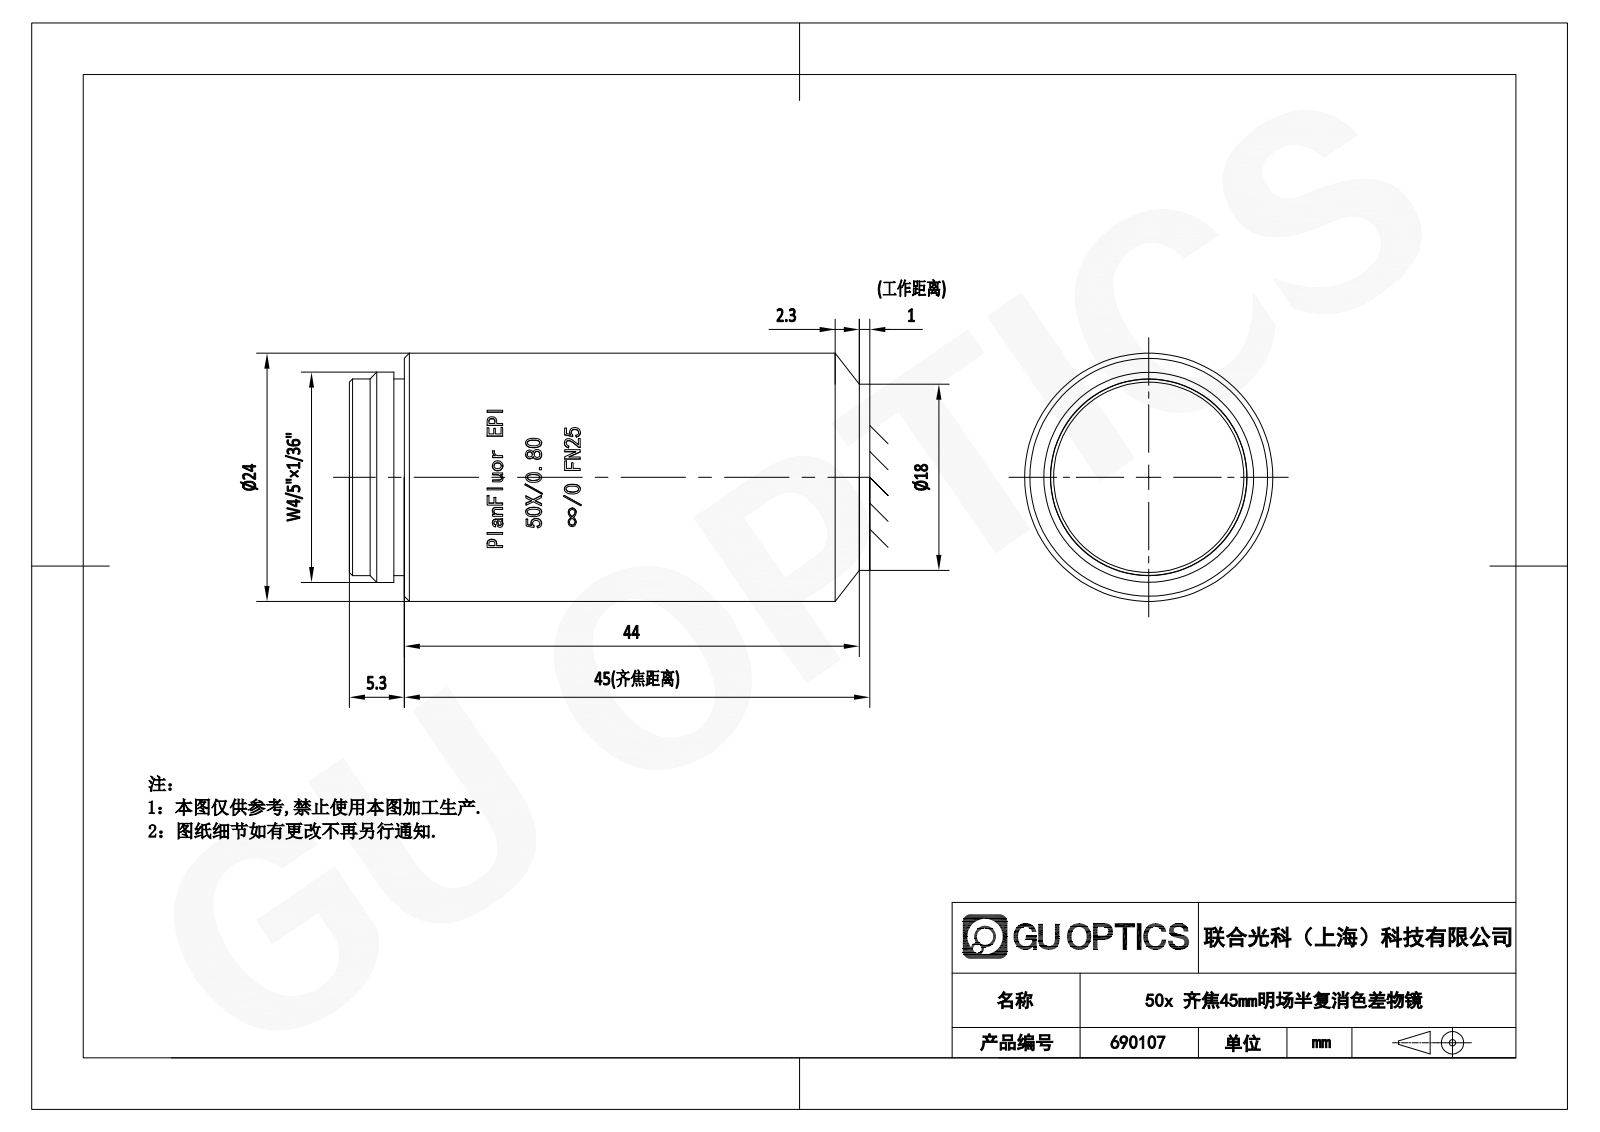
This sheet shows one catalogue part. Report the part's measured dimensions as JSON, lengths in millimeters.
{"part_name": "690107", "step_written_by": "SolidWorks 2020 (CONFIG_CONTROL_DESIGN)", "units": "millimeters", "bodies": {"solids": 1, "faces": 298, "planar": 123, "cylindrical": 47, "other": 128}, "overall_size": [49.3, 24.05, 24], "volume_mm3": 21232, "surface_area_mm2": 4455, "round_bosses_or_shafts": [[24, 1], [20.32, 1], [19, 1]], "partial_cylinders_radius": [[12.05, 1]], "face_to_face_distances": [49.3, 5.3, 44, 4.3, 1, 45, 2, 2.3, 3.3, 47.3]}
